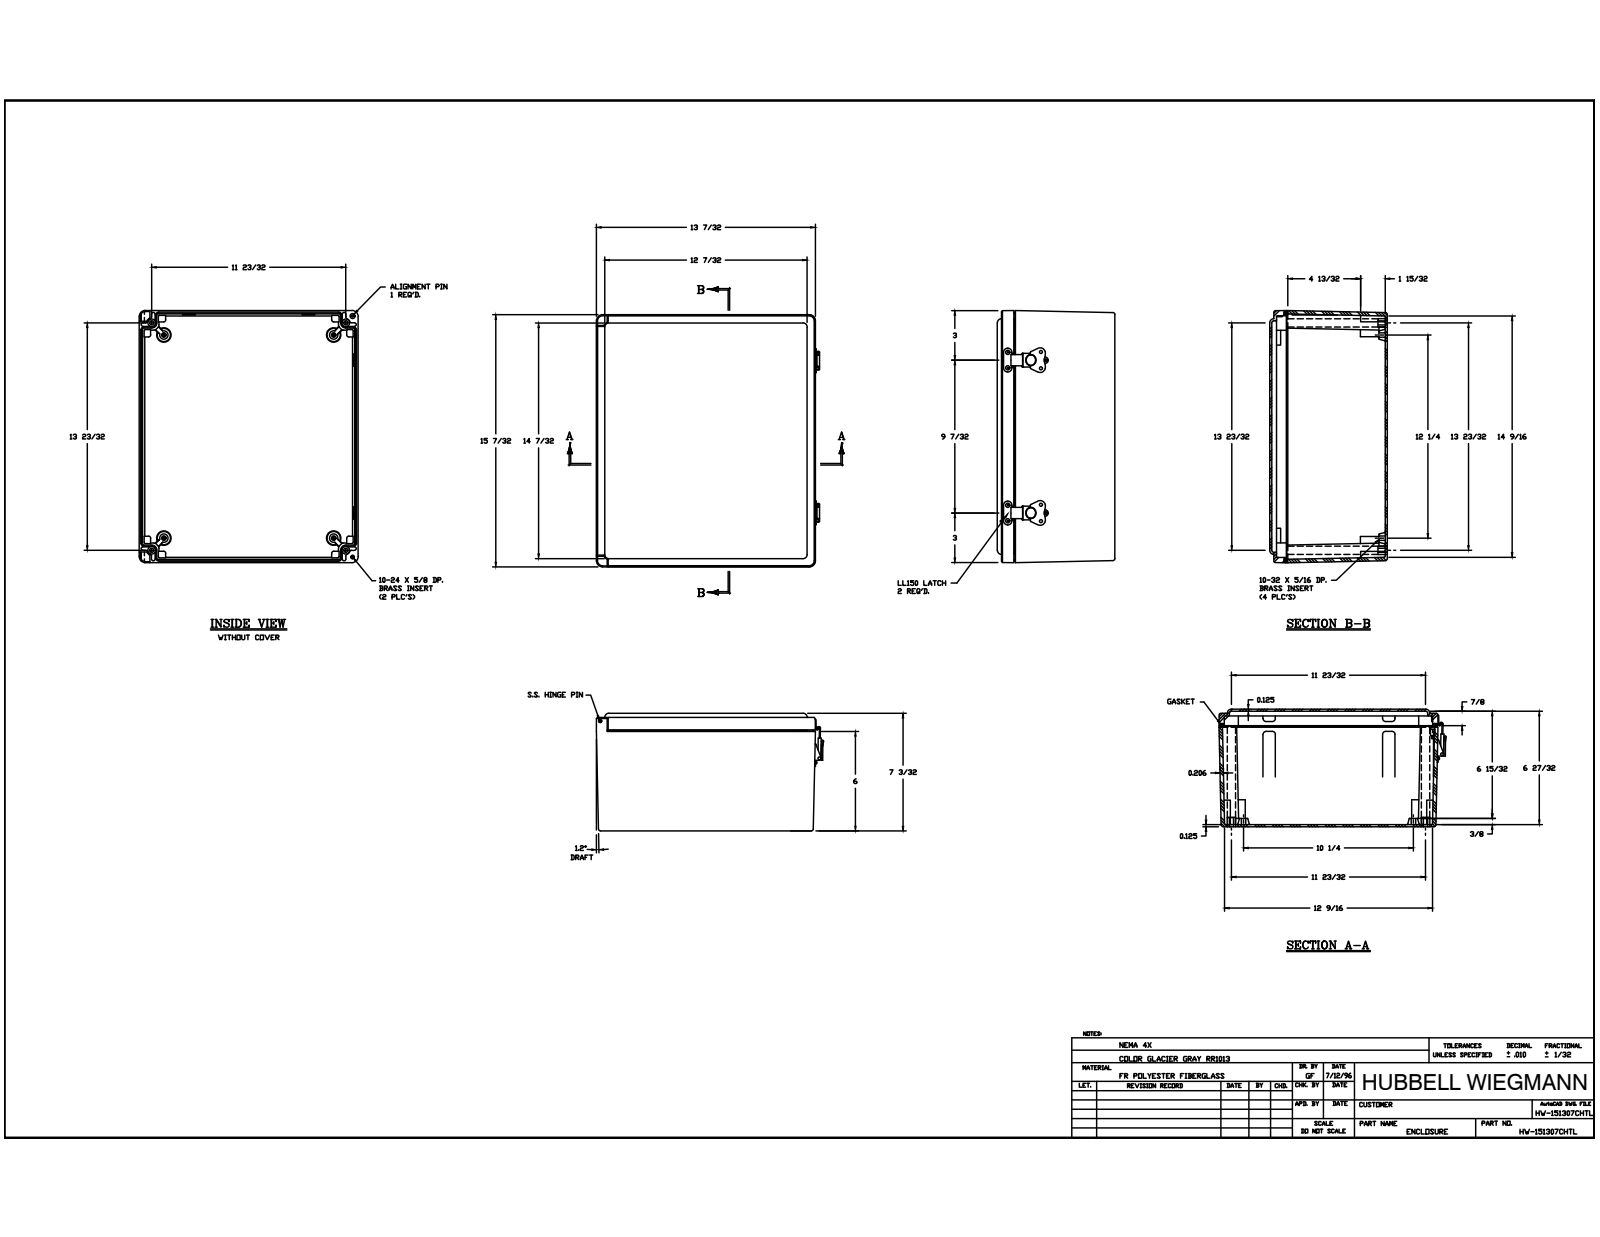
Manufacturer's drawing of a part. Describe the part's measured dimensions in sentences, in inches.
The part is named "WP1513HLLBOX; 0.3125-18 X 0.563 DP BRASS INSERT; 10-32 X0.3125 DP BRASS INSERT; 10-24 X 0.625 DP BRASS INSERT (+8 more)". Its 3-D file was written by "Autodesk Inventor 2014 (AUTOMOTIVE_DESIGN)". It is 41 solids with 1502 faces: 527 planar, 553 cylindrical and 422 other. Overall it measures 15.22 by 13.724 by 7.094 inches. Its volume is 139.8 cubic inches and its surface area 1 707 square inches. Round holes: 8 of diameter 0.104, 8 of diameter 0.14, 6 of diameter 0.187, 6 of diameter 0.281, 4 of diameter 0.13, 4 of diameter 0.156, 4 of diameter 0.313, 4 of diameter 0.531, 2 of diameter 0.096, 2 of diameter 0.098, 2 of diameter 0.145, 2 of diameter 0.156. Round bosses or shafts: 2 of diameter 0.6, 2 of diameter 0.375, 2 of diameter 0.371, 2 of diameter 0.234, 2 of diameter 0.095, 1 of diameter 0.299, 1 of diameter 0.2, 1 of diameter 0.185. Partial cylindrical surfaces (rounded edges, fillets, slot ends): 71 of radius 0.02, 71 of radius 0.031, 41 of radius 0.125, 31 of radius 0.063, 28 of radius 0.01, 12 of radius 0.25, 12 of radius 0.313, 10 of radius 0.187. The main face-to-face distances are 0.125, 6.969, 0.186, 7.094, 6.844, 0.125, 0.25, 6.844, 6.719, 0.75. The hole center spacings are 9.187, 0.506, 0.841, 1.039, 11.01, 13.007, 17.009, 0.528.
